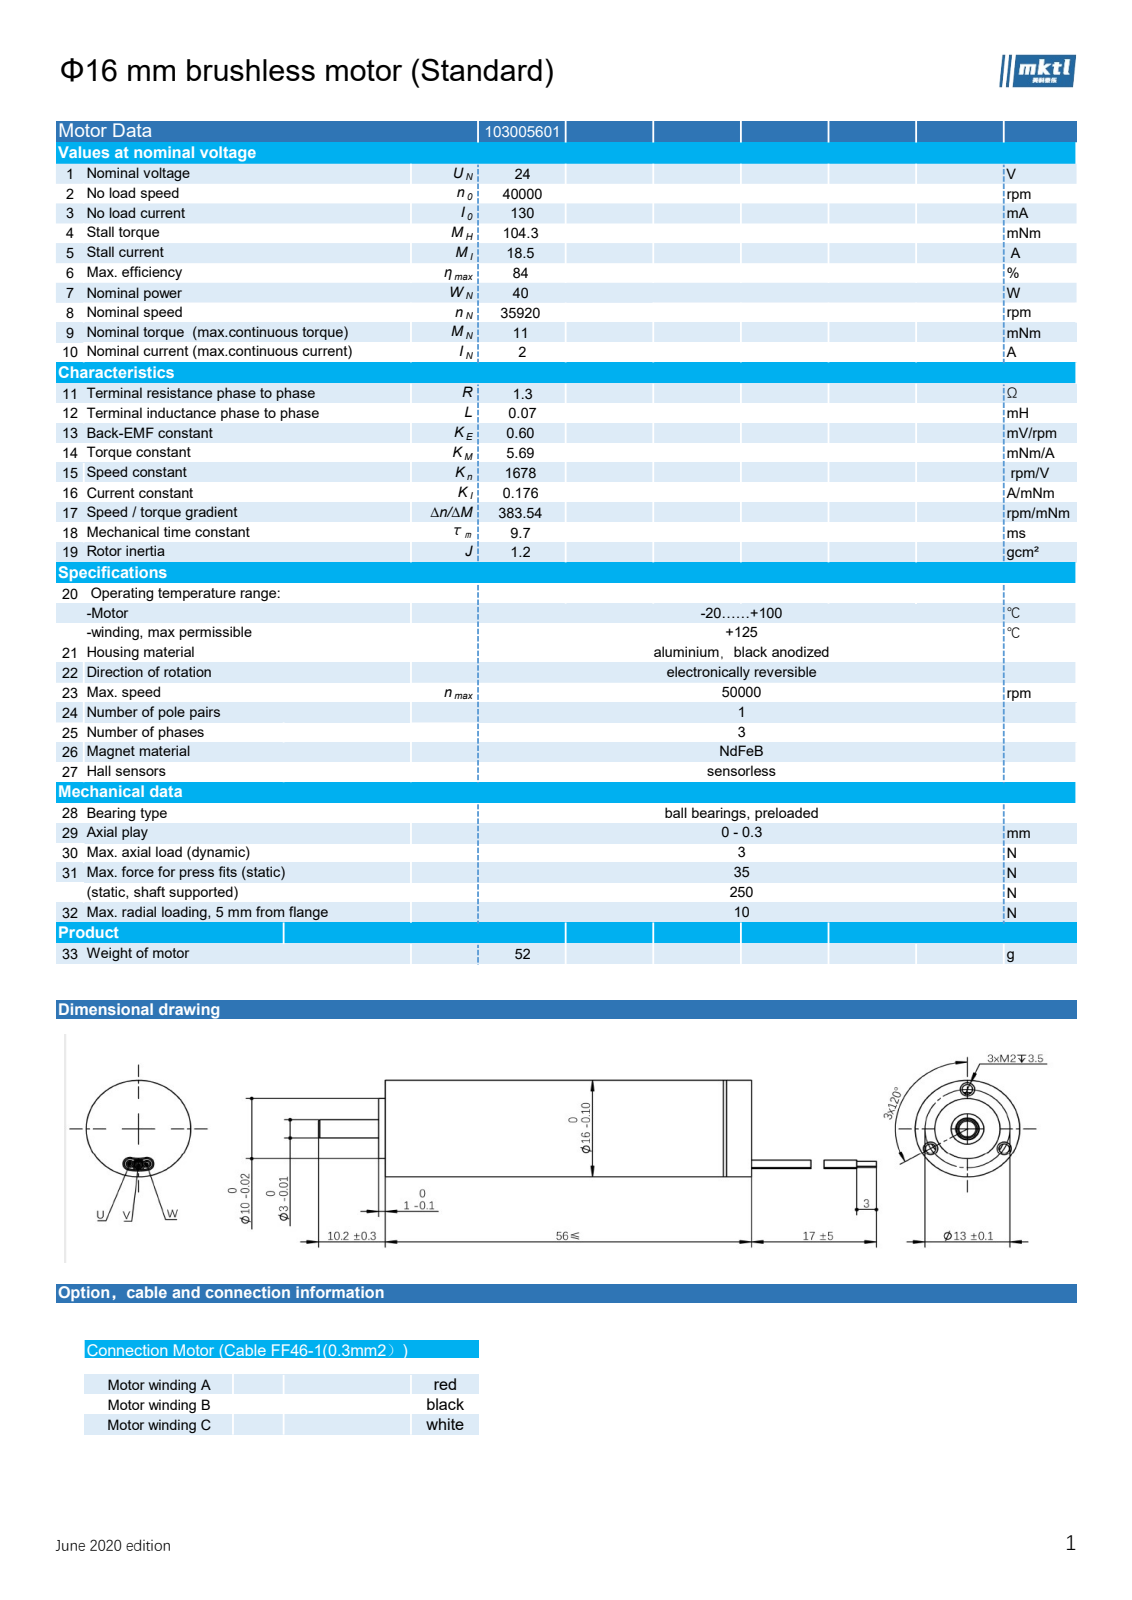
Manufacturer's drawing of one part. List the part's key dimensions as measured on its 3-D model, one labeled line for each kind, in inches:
Part name (STEP PRODUCT): 103005601
STEP written by: SolidWorks 2018 (CONFIG_CONTROL_DESIGN)
Units: inches
Bodies: 215 solids, 1543 faces (468 planar, 989 cylindrical, 86 other)
Overall size (bounding box): 2.957 × 0.63 × 0.63
Volume: 0.602 in³ · Surface area: 76.39 in²
Round holes (diameter × count): ⌀0.059 ×4, ⌀0.063 ×3, ⌀0.118 ×1, ⌀0.122 ×1, ⌀0.197 ×1, ⌀0.335 ×1, ⌀0.346 ×1, ⌀0.425 ×1, ⌀0.433 ×1, ⌀0.445 ×1, ⌀0.472 ×1, ⌀0.555 ×1
Round bosses / shafts (diameter × count): ⌀0.047 ×7, ⌀0.031 ×3, ⌀0.012 ×3, ⌀0.63 ×1, ⌀0.591 ×1, ⌀0.587 ×1, ⌀0.394 ×1, ⌀0.315 ×1
Partial cylindrical surfaces — rounded edges, fillets, slot ends (radius × count): R0.02 ×12, R0.033 ×2, R0.203 ×1, R0.226 ×1, R0.256 ×1, R0.266 ×1, R0.27 ×1
Main face-to-face distances: 0.039, 0.079, 1.299, 0.016, 0.118, 0.024, 0.031, 1.339, 1.26, 1.291
Hole centre spacings: 0.247, 0.236, 0.256, 0.443, 0.492, 0.246, 0.409, 0.409
